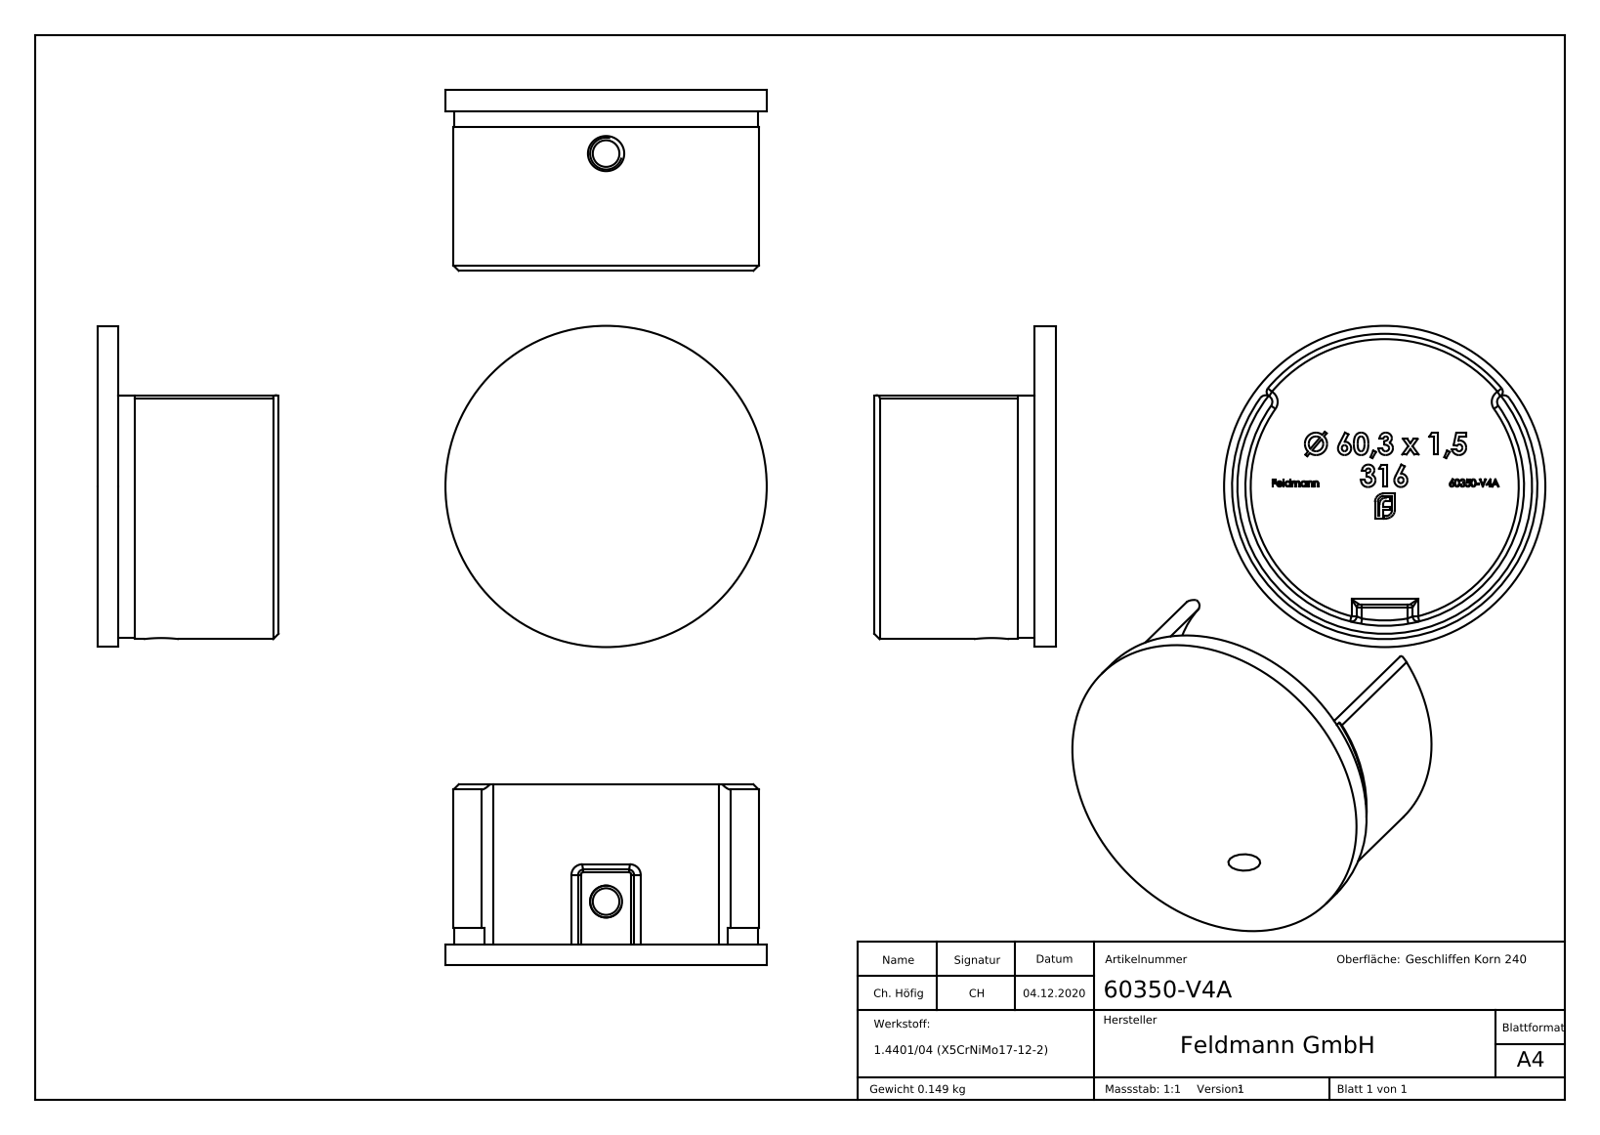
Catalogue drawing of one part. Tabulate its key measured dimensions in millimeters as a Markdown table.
| quantity | value |
| --- | --- |
| part name | 60350-V4A |
| STEP written by | SolidWorks 2018 (CONFIG_CONTROL_DESIGN) |
| units | millimeters |
| bodies | 1 solid, 473 faces (232 planar, 26 cylindrical, 215 other) |
| overall size | 60.3 × 60.3 × 34 |
| volume | 18 658 mm³ |
| surface area | 14 114 mm² |
| round holes (diameter × count) | 5 × 1 |
| round bosses / shafts (diameter × count) | 60.3 × 1 |
| partial cylindrical surfaces (radius × count) | 1 × 7, 0.5 × 3, 1.25 × 2, 26.15 × 1, 28.45 × 1, 28.65 × 1 |
| main face-to-face distances | 3, 4, 1, 30, 31, 34, 2.9, 31.1, 1.1, 27 |
